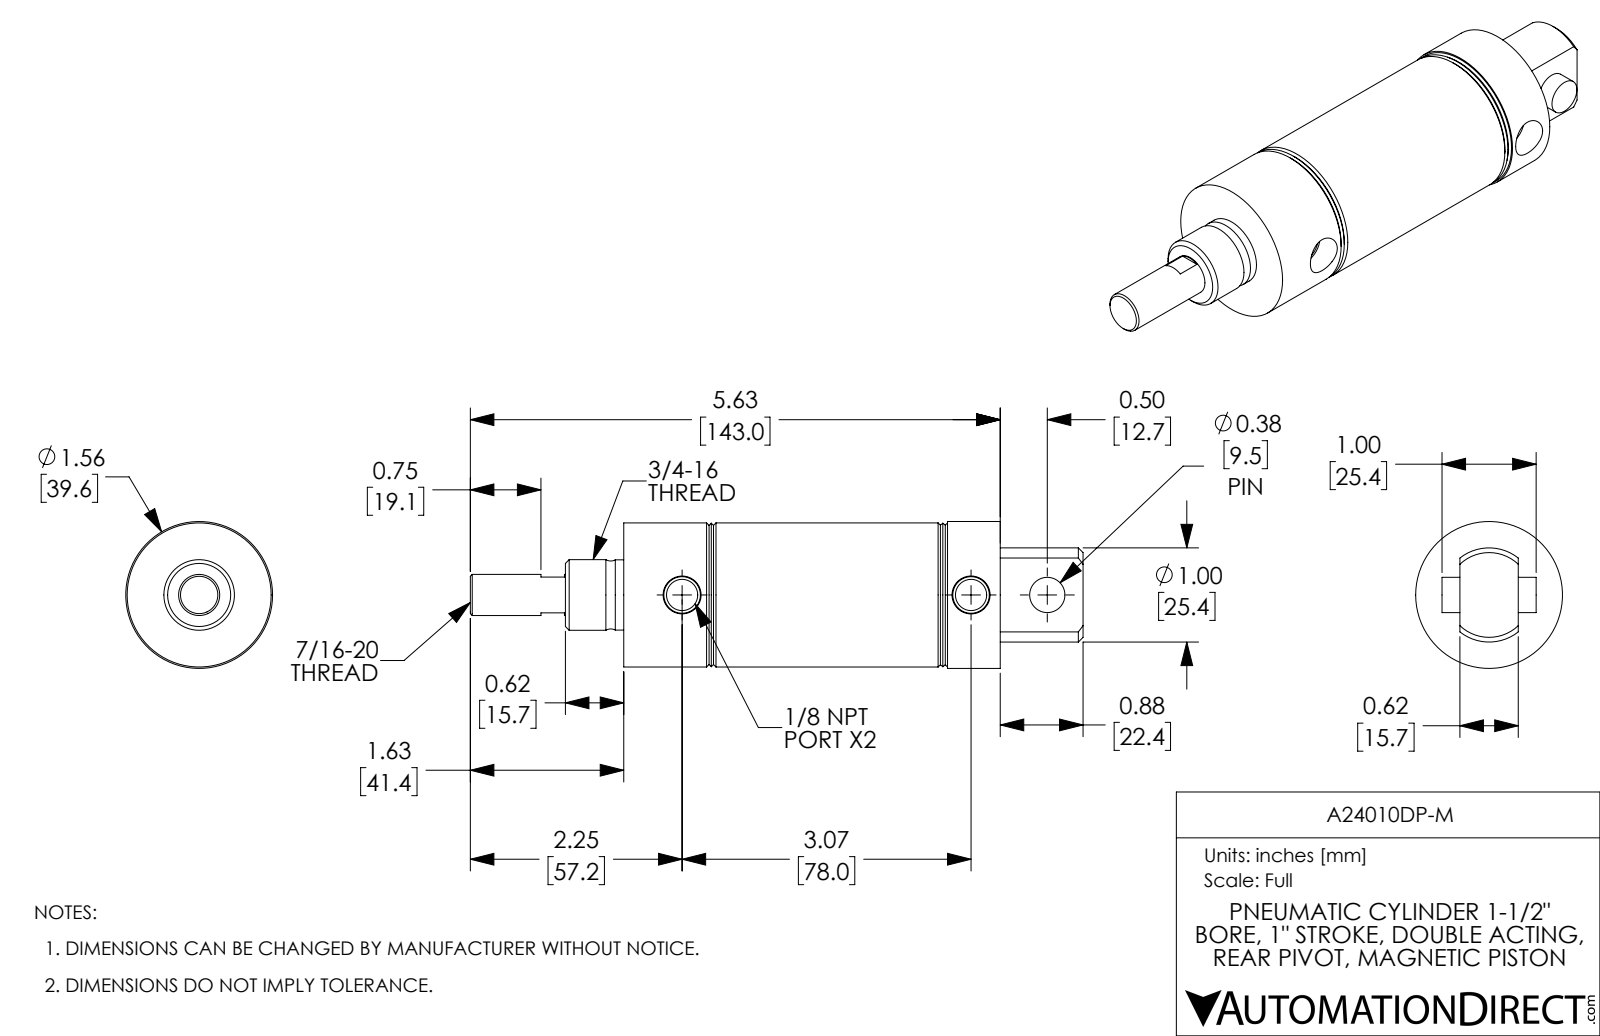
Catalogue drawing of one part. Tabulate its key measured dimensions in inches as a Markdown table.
| quantity | value |
| --- | --- |
| part name | A24010DP-M-Rod; A24010DP-M-Pin; A24010DP-M; A24010DP-M-MainBody |
| STEP written by | SolidWorks 2017 (AUTOMOTIVE_DESIGN) |
| units | inches |
| bodies | 3 solids, 84 faces (22 planar, 28 cylindrical, 34 other) |
| overall size | 6.51 × 1.56 × 1.56 |
| volume | 6.63 in³ |
| surface area | 54.38 in² |
| round holes (diameter × count) | 0.332 × 2, 0.375 × 1, 0.437 × 1, 1.5 × 1 |
| round bosses / shafts (diameter × count) | 1.56 × 1, 1.53 × 1, 0.75 × 1, 0.746 × 1 |
| partial cylindrical surfaces (radius × count) | 0.5 × 1 |
| main face-to-face distances | 1.25, 2.75, 1, 1.5, 0.5, 2.25, 1.75, 4, 0.62, 0.88 |
| hole center spacings | 0.81, 3.07, 3.88 |
